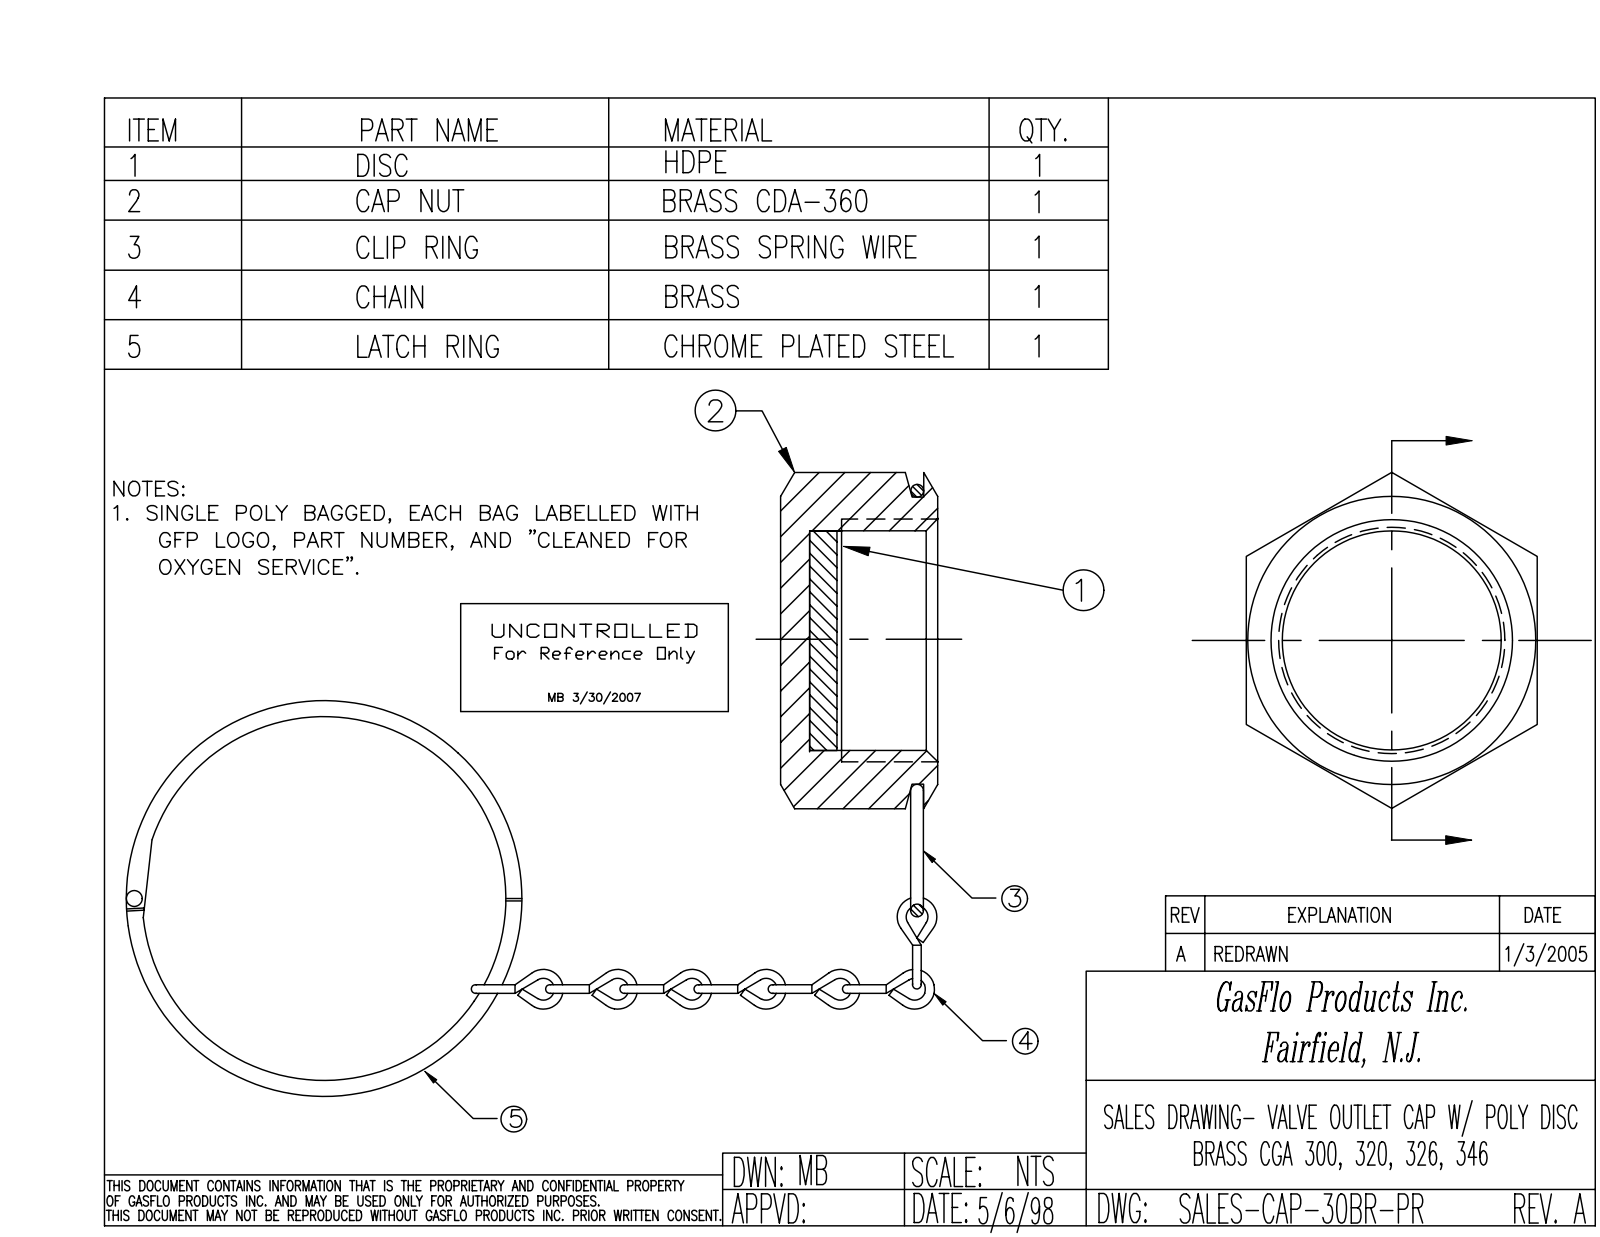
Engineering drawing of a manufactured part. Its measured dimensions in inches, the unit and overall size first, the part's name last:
Units: inches
Overall size (bounding box): 4.489 × 2.074 × 1.125
Round holes (diameter × count): ⌀0.063 ×1, ⌀0.757 ×1
Round bosses / shafts (diameter × count): ⌀0.063 ×30, ⌀0.993 ×1, ⌀0.757 ×1, ⌀0.1 ×1
Partial cylindrical surfaces — rounded edges, fillets, slot ends (radius × count): R0.005 ×24, R0.25 ×4, R0.01 ×2
Main face-to-face distances: 0.1, 1, 0.194, 0.094, 0.54, 0.44, 0.346, 0.478, 0.378, 0.283
Volume: 0.377 in³ · Surface area: 10.91 in²
Bodies: 13 solids, 307 faces (56 planar, 116 cylindrical, 135 other)
Part name (STEP PRODUCT): PRT-000010; PRT-000160; ASY-000291; PRT-002255_SMALL PIN (+5 more)
STEP written by: SolidWorks 2018 (CONFIG_CONTROL_DESIGN)
